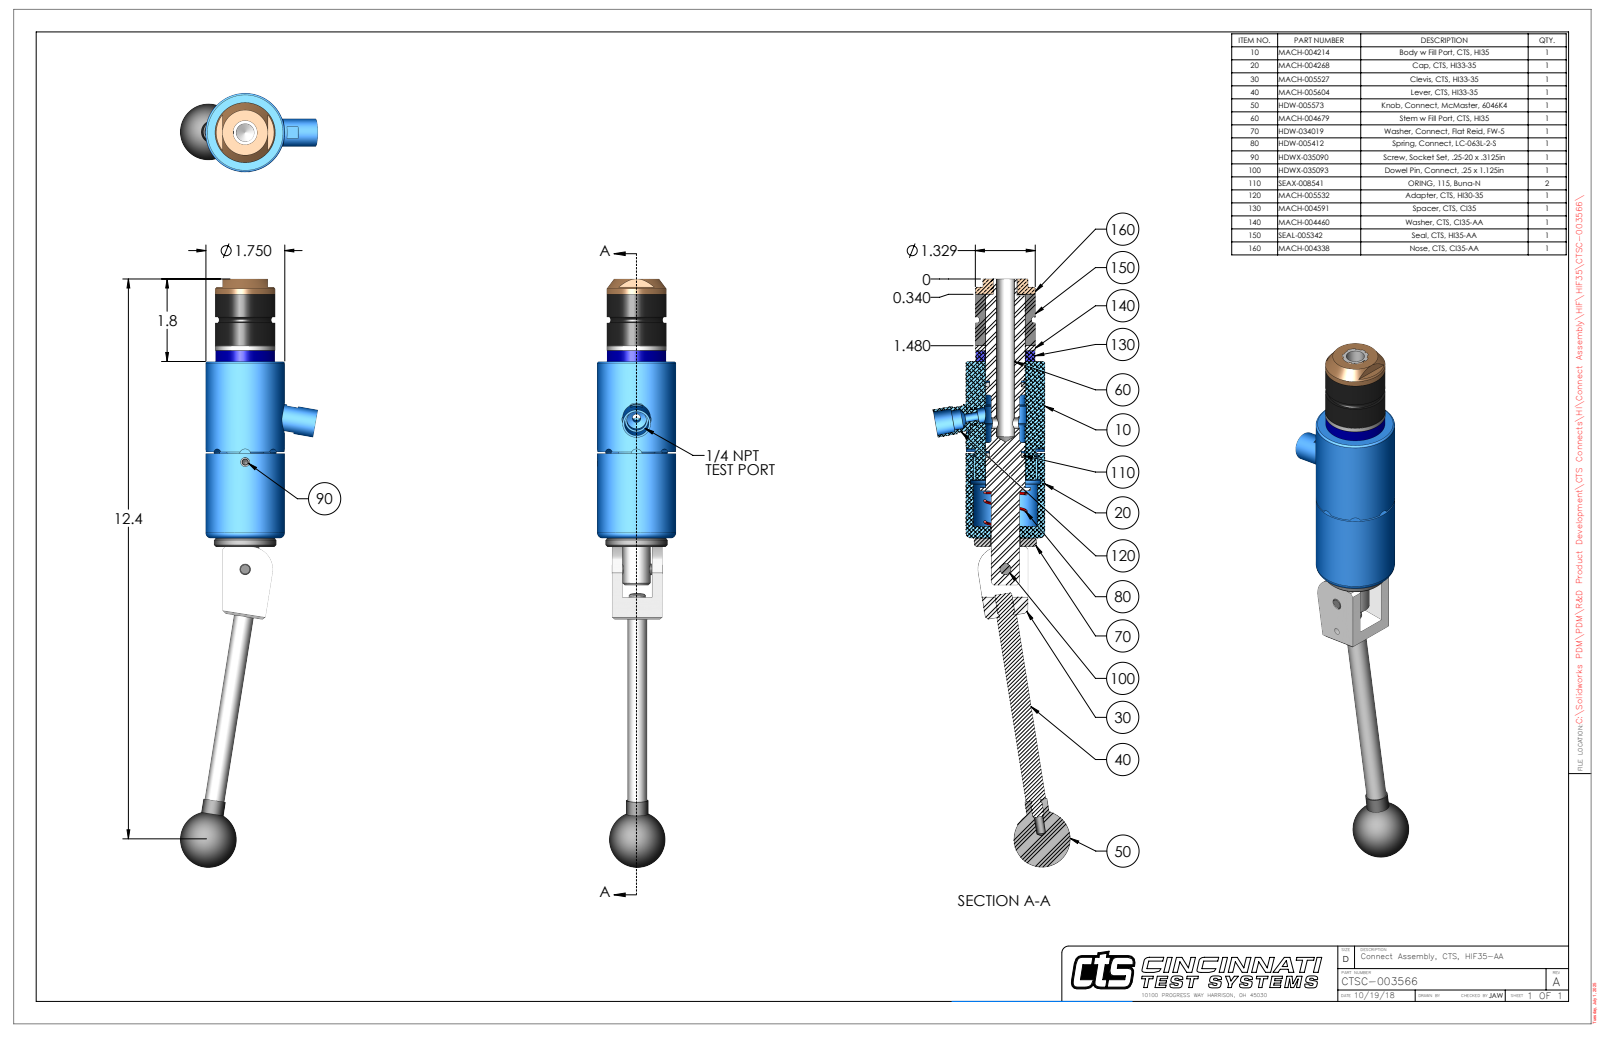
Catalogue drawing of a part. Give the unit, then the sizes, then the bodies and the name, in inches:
Units: inches
Overall size (bounding box): 13.042 × 3.043 × 1.75
Round holes (diameter × count): ⌀0.201 ×2, ⌀0.15 ×1, ⌀0.187 ×1, ⌀0.249 ×1, ⌀0.25 ×1, ⌀0.251 ×1, ⌀0.313 ×1, ⌀0.406 ×1, ⌀0.438 ×1, ⌀0.531 ×1, ⌀0.635 ×1, ⌀0.656 ×1
Round bosses / shafts (diameter × count): ⌀0.25 ×2, ⌀1.75 ×1, ⌀1.38 ×1, ⌀1.329 ×1, ⌀1.312 ×1, ⌀0.869 ×1, ⌀0.625 ×1, ⌀0.62 ×1
Partial cylindrical surfaces — rounded edges, fillets, slot ends (radius × count): R0.125 ×4, R0.029 ×2, R0.166 ×1, R0.166 ×1, R0.242 ×1, R0.33 ×1, R0.5 ×1, R0.695 ×1
Main face-to-face distances: 3.915, 1.49, 5.405, 1.14, 0.35, 4.265, 1.25, 0.11, 0.24, 4.155
Hole centre spacings: 0.74, 2.376, 3.116
Volume: 14.62 in³ · Surface area: 89.38 in²
Bodies: 10 solids, 297 faces (107 planar, 124 cylindrical, 66 other)
Part name (STEP PRODUCT): CTSC-003566
STEP written by: SolidWorks 2023 (AUTOMOTIVE_DESIGN)
